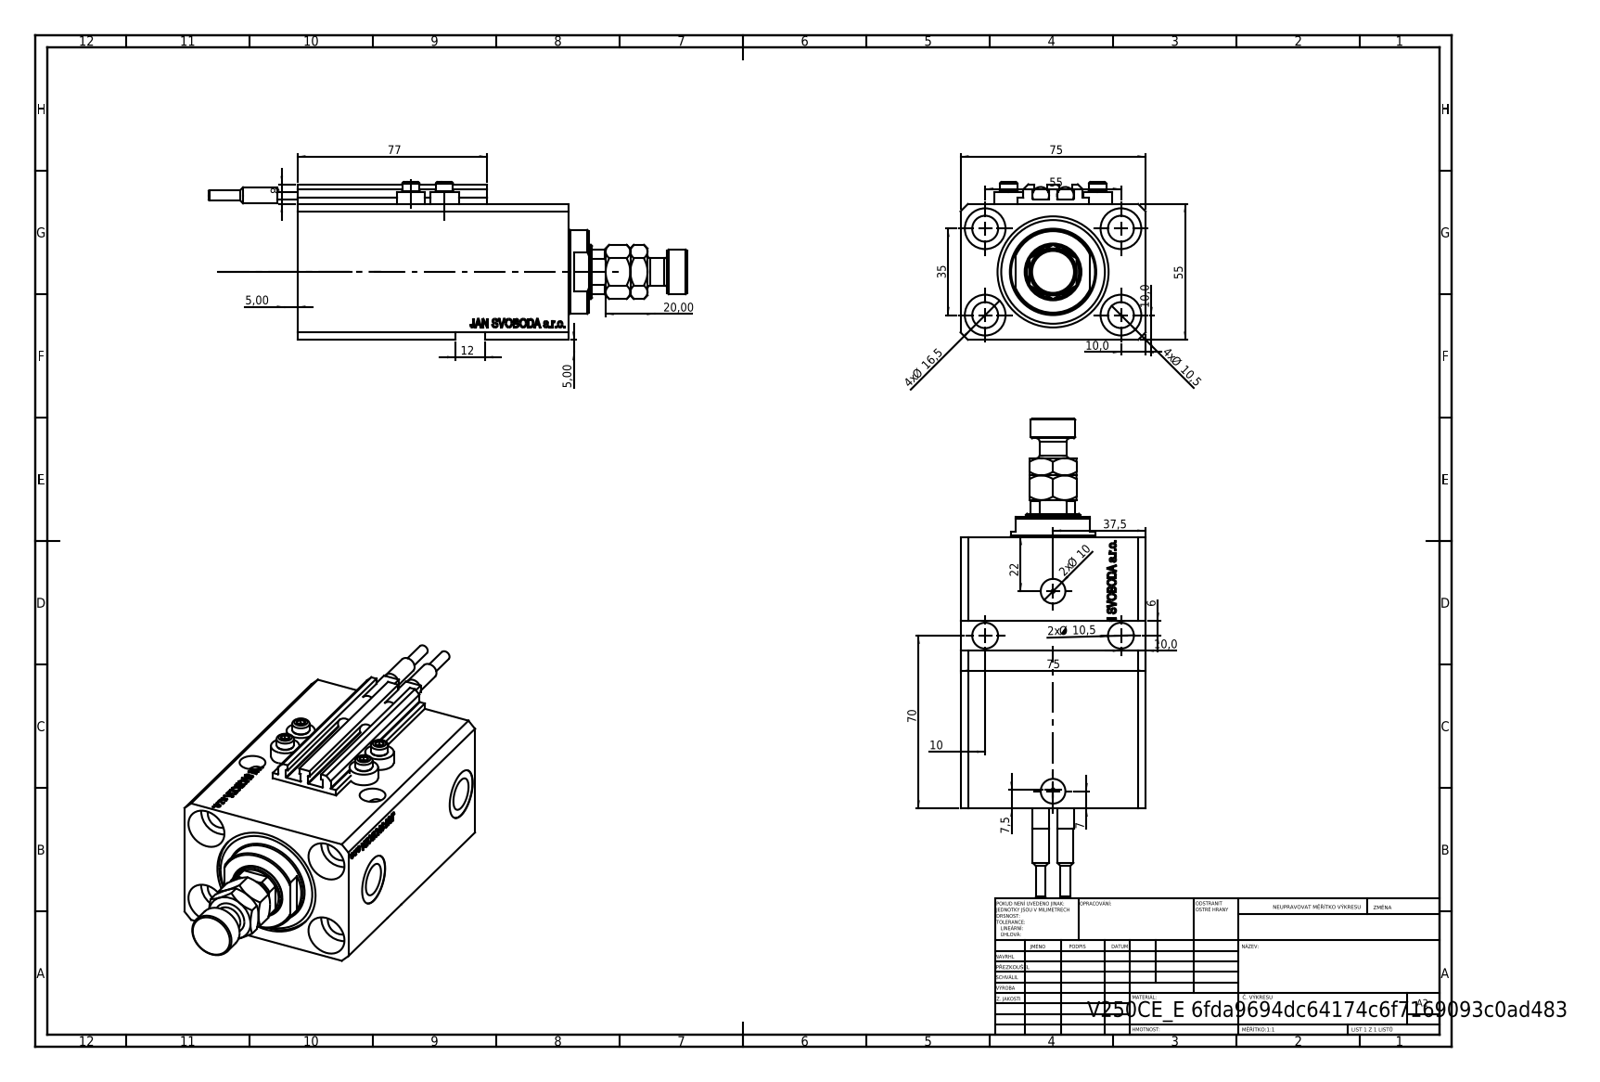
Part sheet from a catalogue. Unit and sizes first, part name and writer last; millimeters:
Units: millimetres
Overall size (bounding box): 193.9 × 75 × 64
Round holes (diameter × count): ⌀10.5 ×7, ⌀1.25 ×4, ⌀4 ×4, ⌀16.5 ×4, ⌀10 ×2, ⌀13.16 ×2, ⌀20 ×2, ⌀22 ×1, ⌀32 ×1, ⌀45 ×1
Round bosses / shafts (diameter × count): ⌀11.6 ×4, ⌀7 ×4, ⌀6.8 ×2, ⌀6.5 ×2, ⌀4 ×2, ⌀34 ×1, ⌀18 ×1, ⌀11 ×1
Partial cylindrical surfaces — rounded edges, fillets, slot ends (radius × count): R0.2 ×10, R10.5 ×1
Main face-to-face distances: 55, 75, 3, 110, 57, 82.9, 27.1, 9.9, 73, 100.1
Hole centre spacings: 32.6, 55, 13.6, 14.09, 25.81, 32.87, 33.62, 35
Volume: 399 394 mm³ · Surface area: 102 174 mm²
Bodies: 11 solids, 1168 faces (562 planar, 142 cylindrical, 464 other)
Part name (STEP PRODUCT): SWITCH_V250CE; V250CE_E_Body; MFA; ALLEN BOLT V250CE (+2 more)
STEP written by: SolidWorks 2019 (CONFIG_CONTROL_DESIGN)
